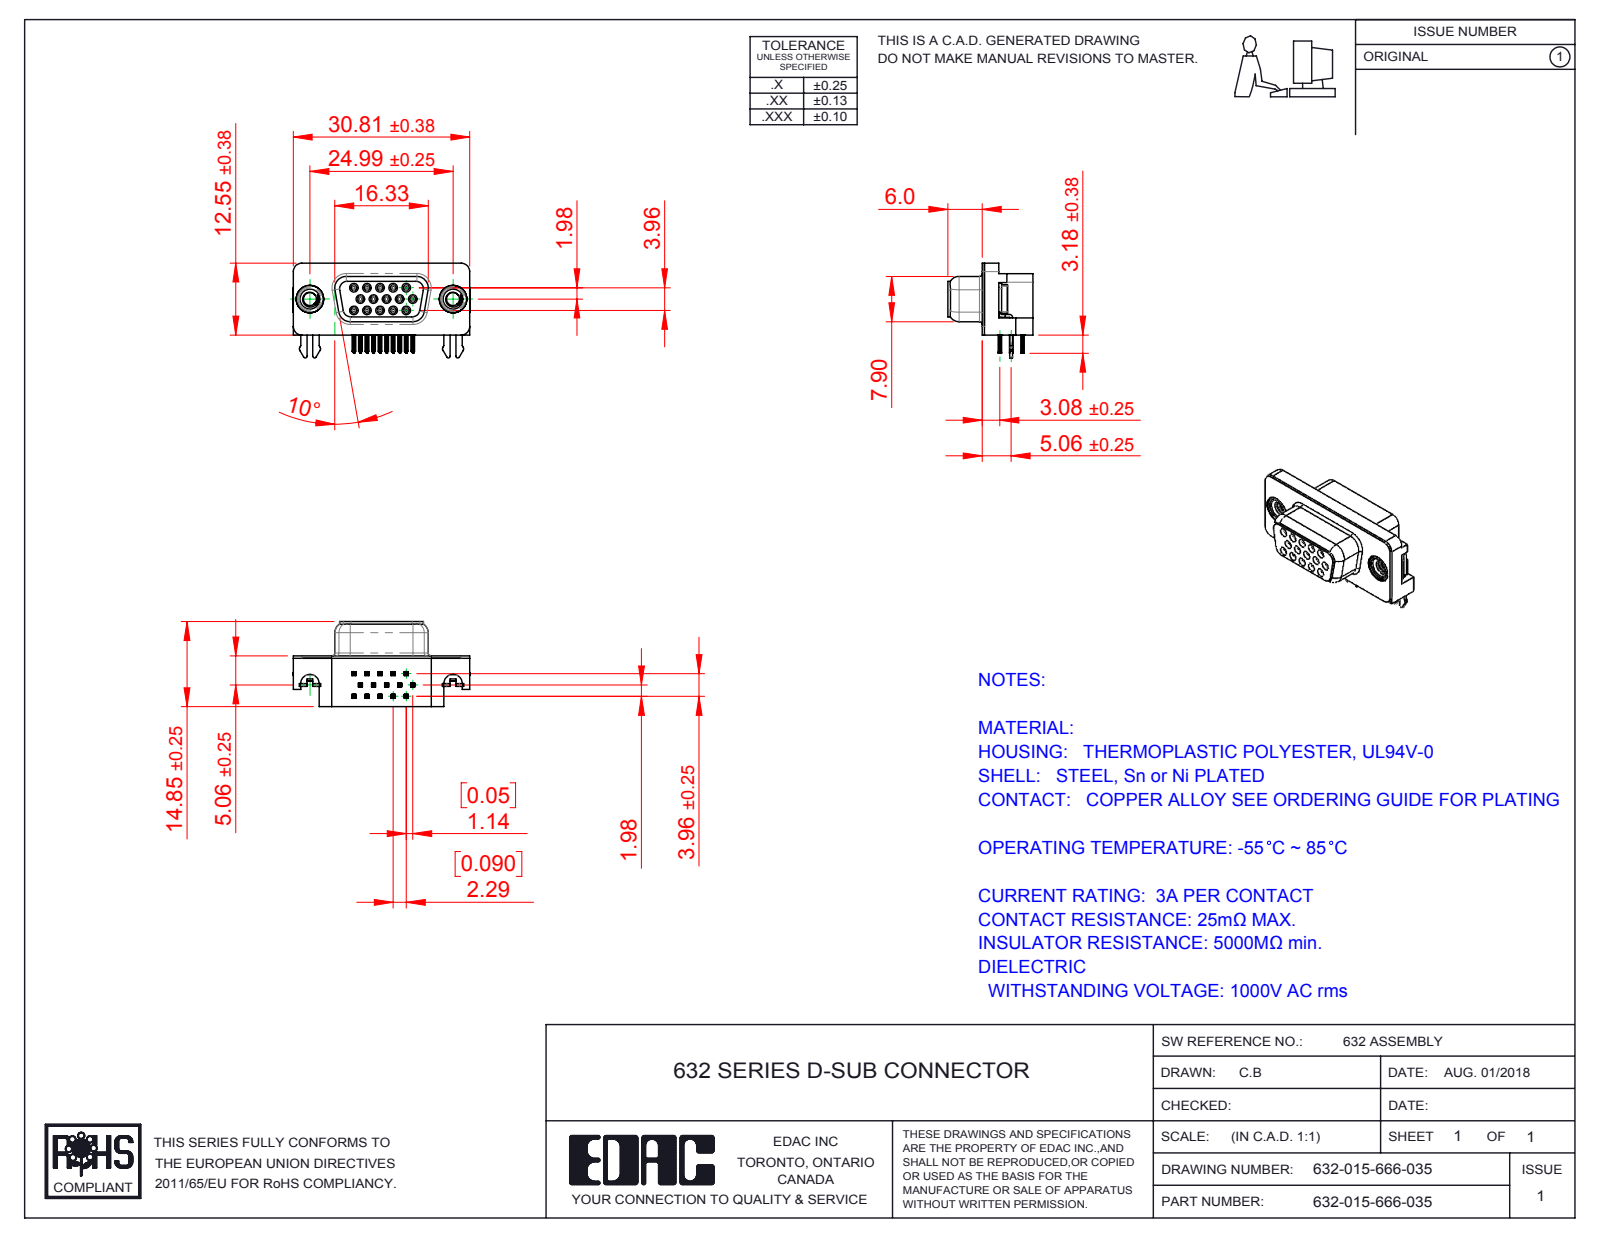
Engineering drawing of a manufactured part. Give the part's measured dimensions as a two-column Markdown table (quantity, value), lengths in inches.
| quantity | value |
| --- | --- |
| part name | 632 Shell_9 Socket; 632 Contact Middle; 632 Contact Bottom; 632 Contact Top (+5 more) |
| STEP written by | SolidWorks 2016 (CONFIG_CONTROL_DESIGN) |
| units | inches |
| bodies | 23 solids, 2426 faces (1006 planar, 654 cylindrical, 766 other) |
| overall size | 1.216 × 0.652 × 0.585 |
| volume | 0.183 in³ |
| surface area | 8.28 in² |
| round holes (diameter × count) | 0.031 × 15, 0.035 × 15, 0.089 × 2, 0.098 × 2, 0.157 × 2, 0.189 × 2, 0.197 × 2 |
| round bosses / shafts (diameter × count) | 0.047 × 15, 0.193 × 2, 0.187 × 2, 0.154 × 2 |
| partial cylindrical surfaces (radius × count) | 0.004 × 120, 0.006 × 60, 0.014 × 30, 0.013 × 15, 0.039 × 11, 0.011 × 10, 0.02 × 10, 0.01 × 8 |
| main face-to-face distances | 0.016, 0.333, 0.348, 0.078, 0.114, 0.234, 0.098, 0.252, 0.264, 0.278 |
| hole center spacings | 0.09, 0.09, 0.156, 0.18, 0.238, 0.156, 0.18, 0.27 |
